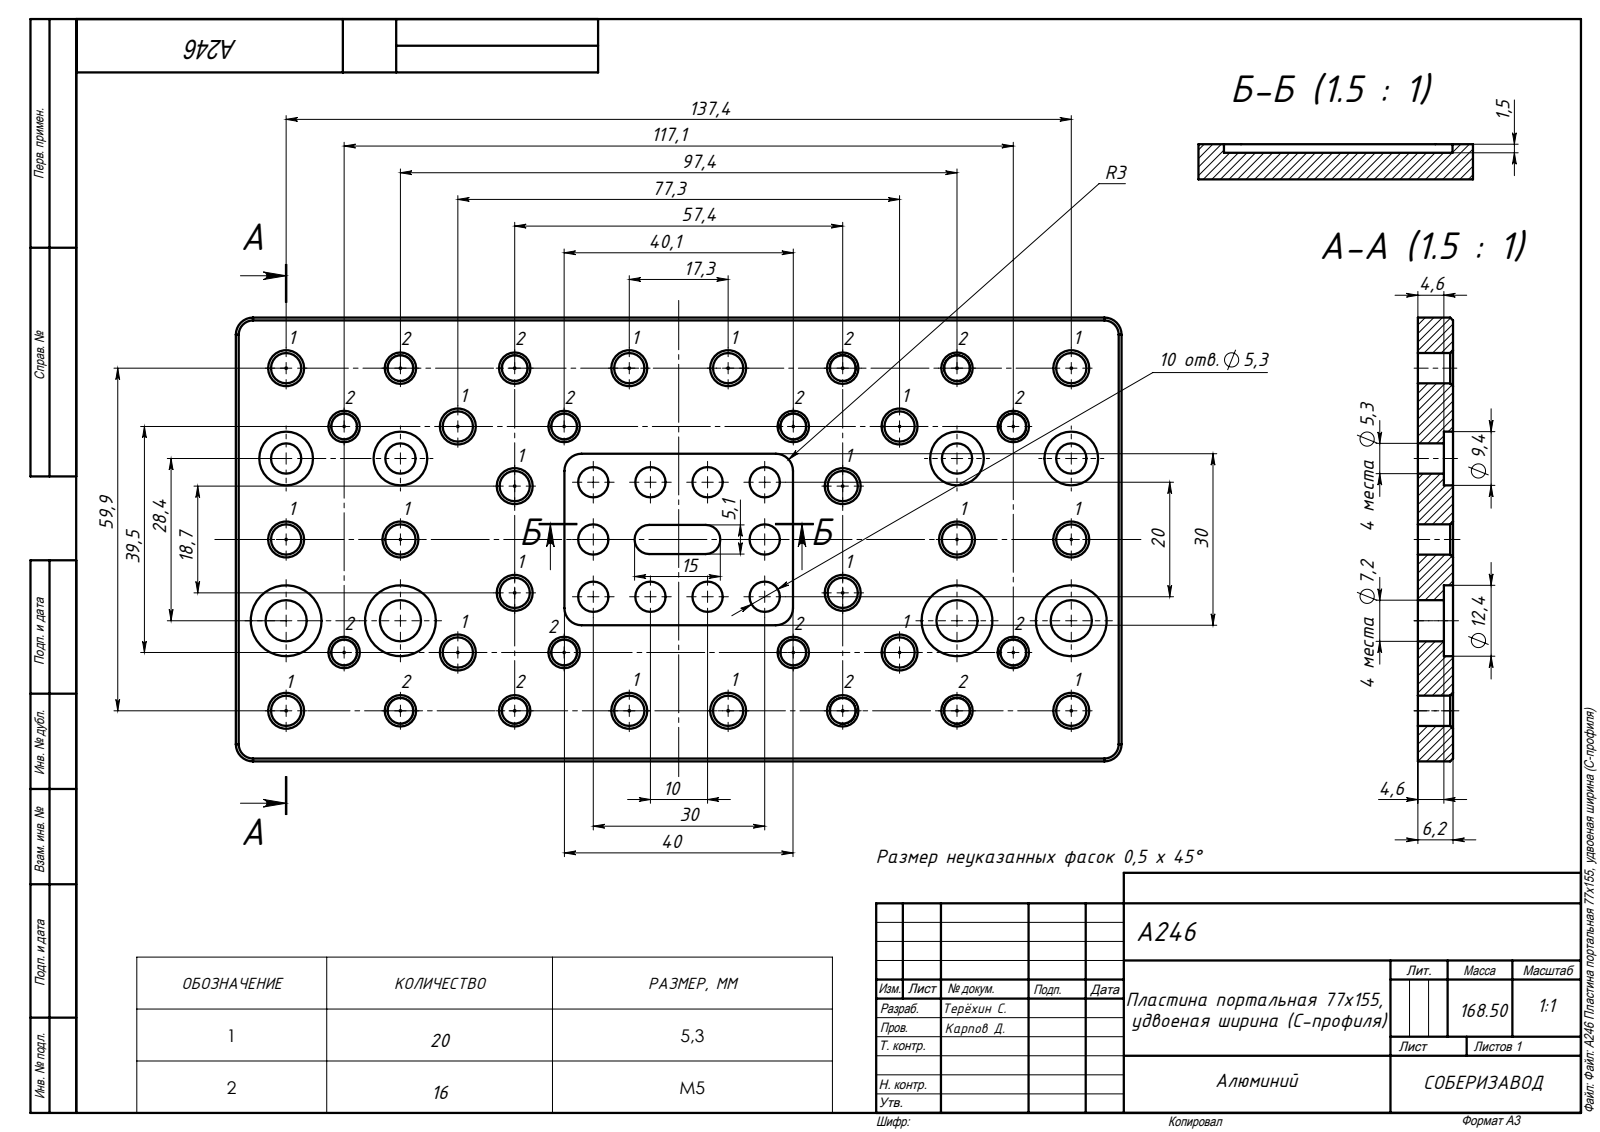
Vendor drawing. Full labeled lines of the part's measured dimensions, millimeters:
Part name (STEP PRODUCT): A246 Пластина портальная 77х155, удвоеная ширина (С-профиля)
STEP written by: SolidWorks 2019 (AUTOMOTIVE_DESIGN)
Units: millimetres
Bodies: 1 solid, 268 faces (25 planar, 135 cylindrical, 108 other)
Overall size (bounding box): 155 × 77.63 × 6.15
Volume: 64 009 mm³ · Surface area: 29 790 mm²
Round holes (diameter × count): ⌀5.3 ×34, ⌀4.5 ×16, ⌀7.2 ×4, ⌀9.4 ×4, ⌀12.4 ×4
Partial cylindrical surfaces — rounded edges, fillets, slot ends (radius × count): R3 ×8, R2.55 ×2
Main face-to-face distances: 6.15, 4.65, 1.5, 77.63, 4.55, 1.6, 155, 12.45, 17.55, 57.5
Hole centre spacings: 20, 10, 22.39, 20.03, 22.37, 28.31, 28.38, 31.63
